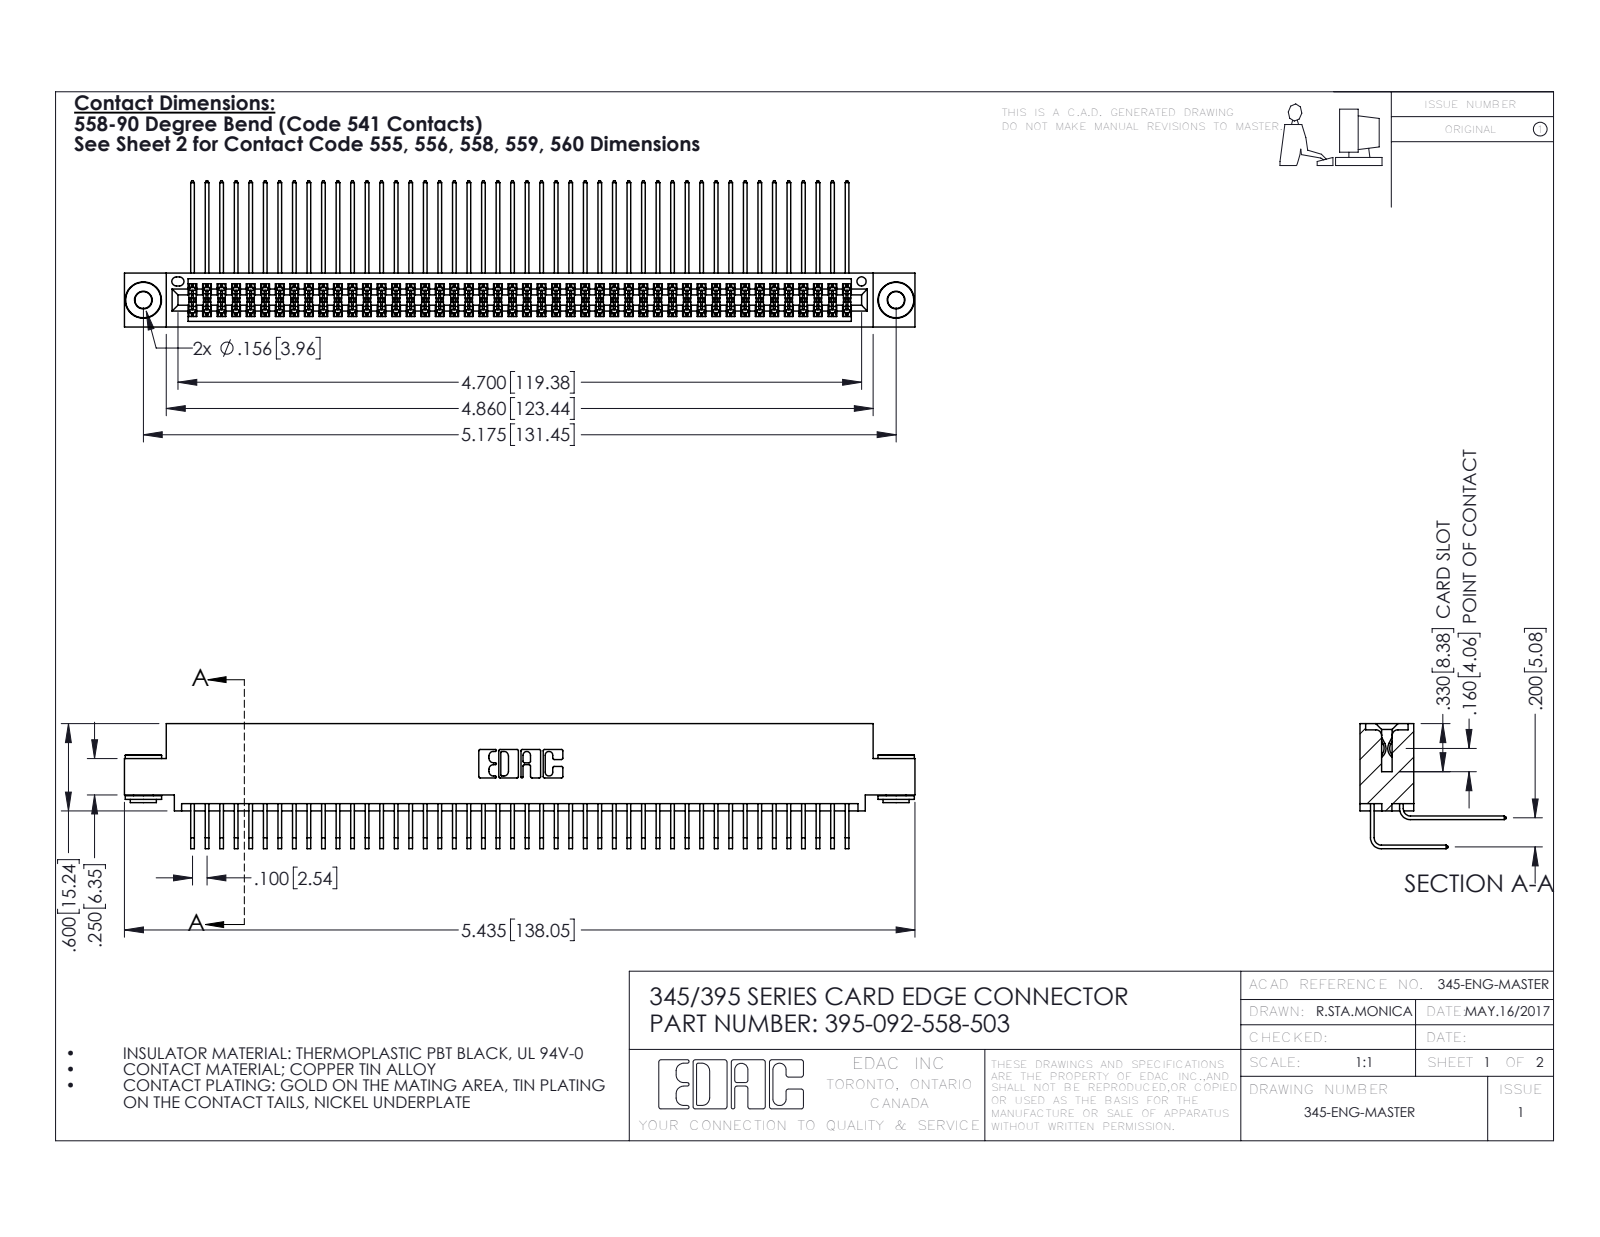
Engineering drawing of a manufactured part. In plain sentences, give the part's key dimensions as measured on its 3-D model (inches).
The part is named "395-092-558-503; 345 Part_0.110 Offset - 0.156 Dia-TH; 345-250-002_345-250-002-102; 345-292-001_558 559 Tail - 1 (+1 more)". Its 3-D file was written by "SolidWorks 2016 (CONFIG_CONTROL_DESIGN)". It is 95 solids with 4952 faces: 3314 planar, 1630 cylindrical and 8 other. Overall it measures 5.435 by 1.005 by 0.859 inches. Its volume is 0.85 cubic inches and its surface area 36.35 square inches. Round holes: 2 of diameter 0.116, 2 of diameter 0.156, 1 of diameter 0.064. Round bosses or shafts: 2 of diameter 0.25, 2 of diameter 0.18, 2 of diameter 0.136. Partial cylindrical surfaces (rounded edges, fillets, slot ends): 139 of radius 0.006, 22 of radius 0.01, 6 of radius 0.007, 6 of radius 0.031, 3 of radius 0.026, 2 of radius 0.014, 2 of radius 0.019, 2 of radius 0.022. The main face-to-face distances are 0.072, 0.298, 0.2, 0.37, 0.025, 0.098, 0.272, 0.225, 0.025, 0.175. The hole center spacings are 0.27, 4.939, 5.175.
